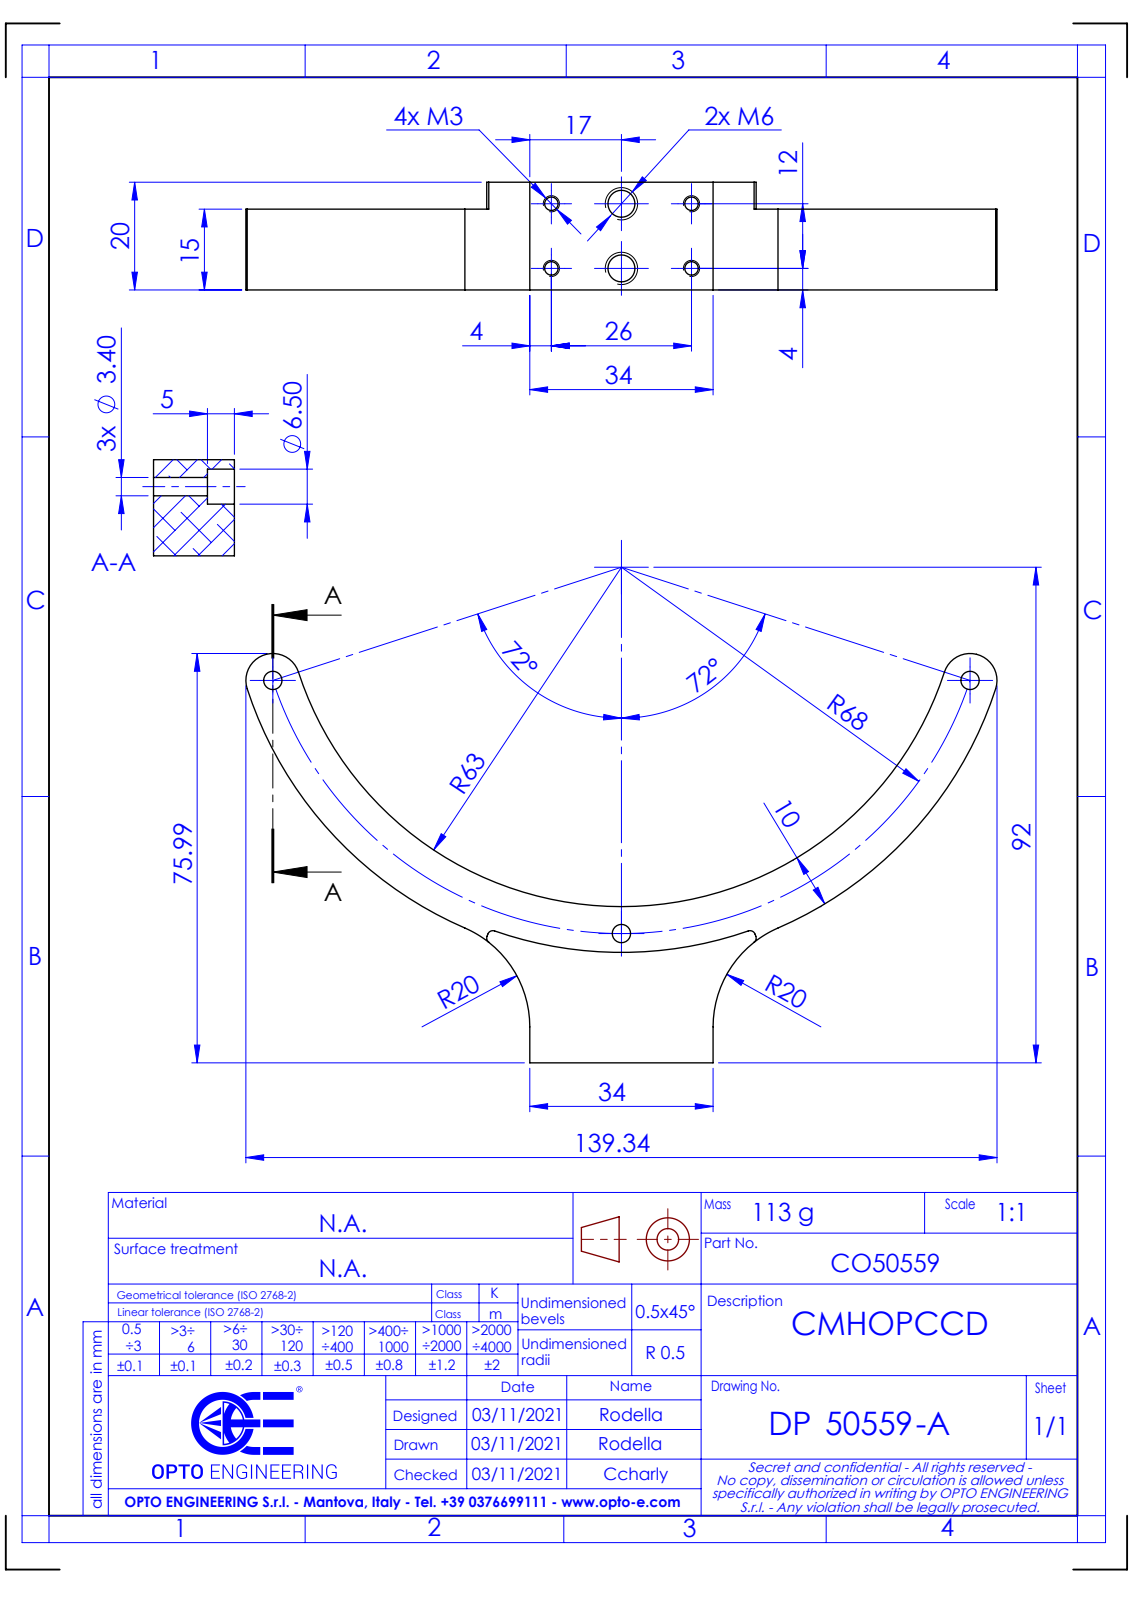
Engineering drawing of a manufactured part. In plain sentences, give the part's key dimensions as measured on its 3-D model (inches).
The part is named "DP50559_CMHOPCCD". Its 3-D file was written by "SolidWorks 2021 (CONFIG_CONTROL_DESIGN)". It is 0 solids with 88 faces: 32 planar, 46 cylindrical and 10 other. Overall it measures 5.486 by 2.992 by 0.787 inches. Round holes: 4 of diameter 0.098, 3 of diameter 0.134, 3 of diameter 0.256, 2 of diameter 0.197. Round bosses or shafts: 3 of diameter 0.118. Partial cylindrical surfaces (rounded edges, fillets, slot ends): 4 of radius 0.039, 2 of radius 0.197, 2 of radius 0.787, 1 of radius 2.48, 1 of radius 2.815, 1 of radius 2.874. The main face-to-face distances are 0.591, 0.197, 0.787, 1.339, 0.709, 0.512, 0.079, 0.101, 0.039, 0.157. The hole center spacings are 0.512, 0.696, 0.472, 1.024, 1.128, 3.147, 5.092.
